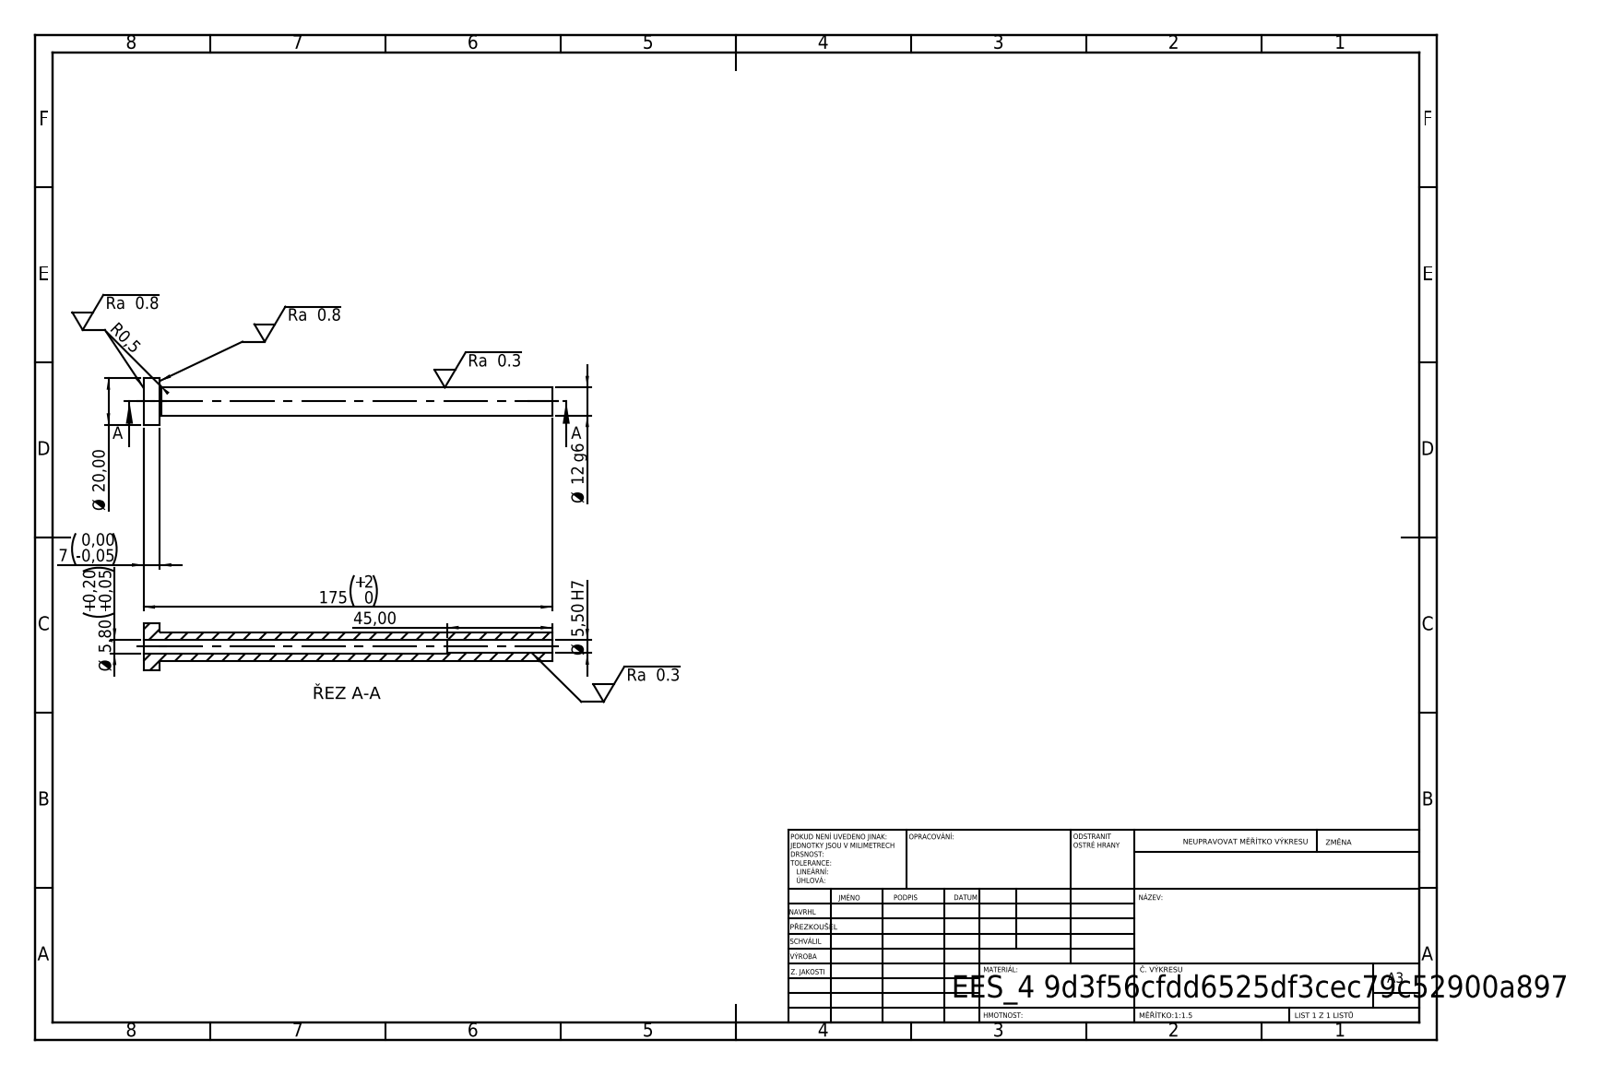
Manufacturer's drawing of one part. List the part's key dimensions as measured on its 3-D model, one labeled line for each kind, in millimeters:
STEP written by: SolidWorks 2019 (CONFIG_CONTROL_DESIGN)
Units: millimetres
Bodies: 1 solid, 14 faces (4 planar, 8 cylindrical, 2 other)
Overall size (bounding box): 175 × 20 × 20
Volume: 16 698 mm³ · Surface area: 10 492 mm²
Round holes (diameter × count): ⌀5.5 ×1, ⌀5.8 ×1
Round bosses / shafts (diameter × count): ⌀20 ×1, ⌀12 ×1
Main face-to-face distances: 7, 175, 168, 130, 123, 45
